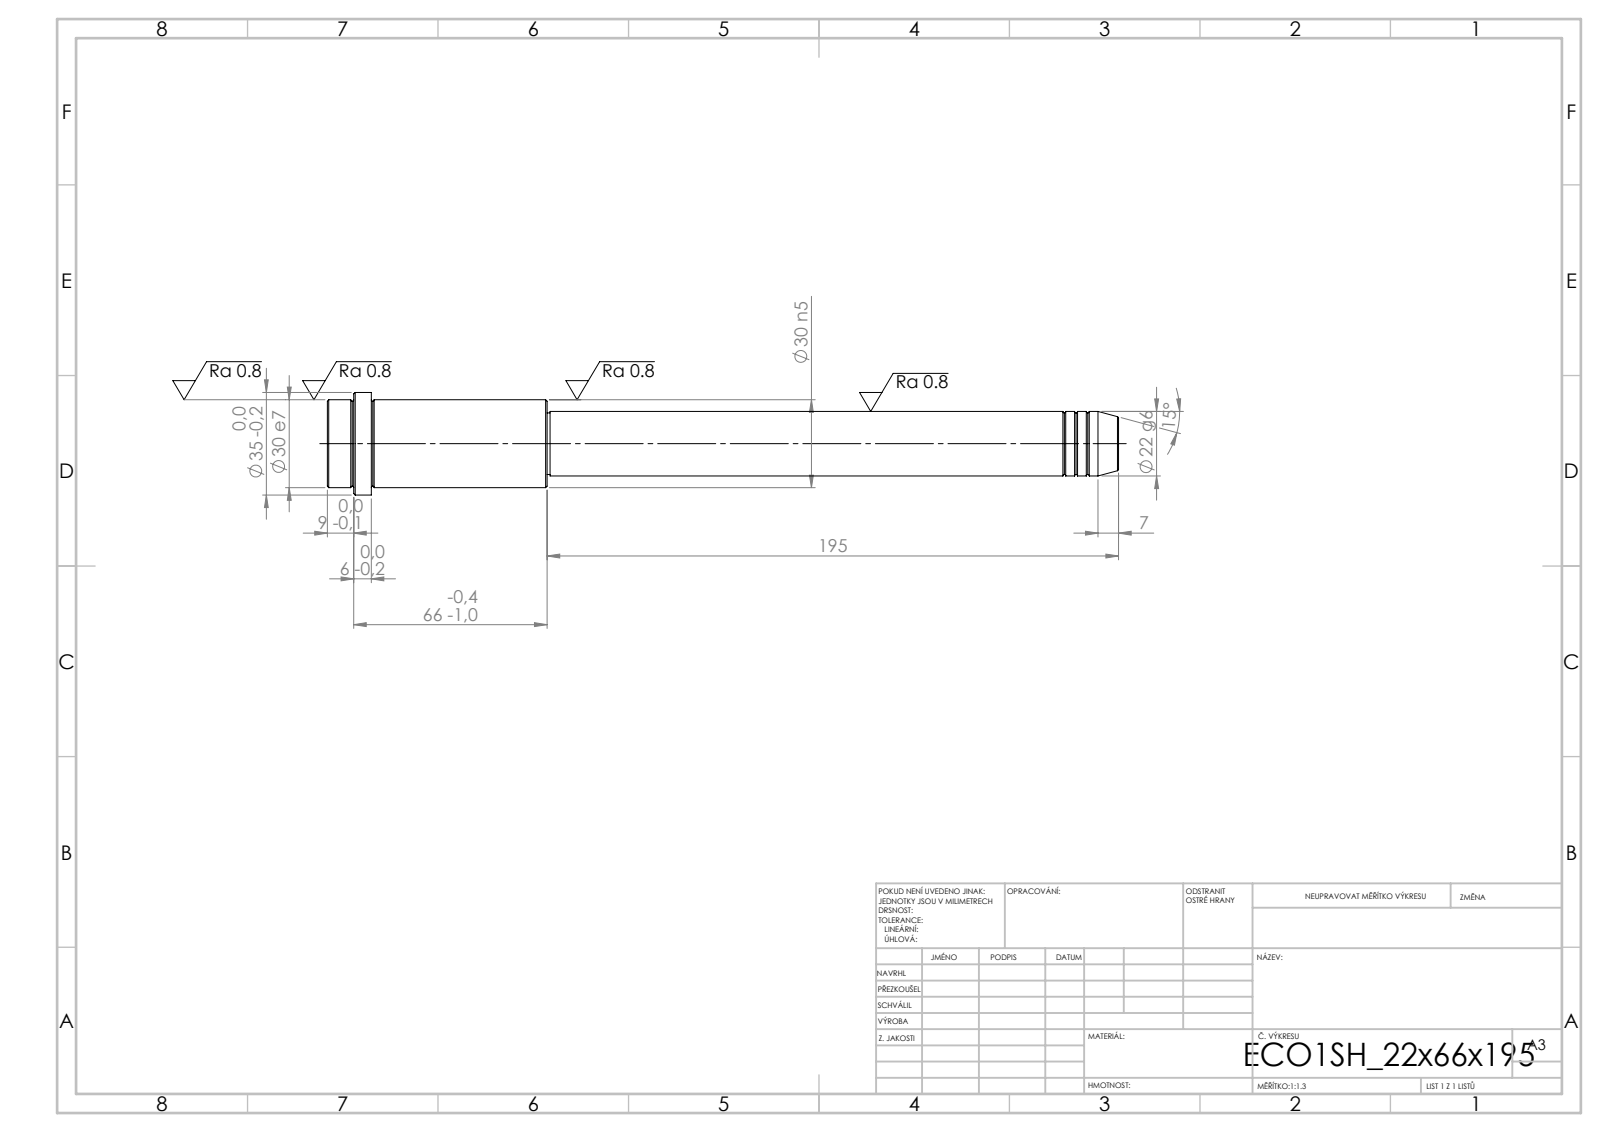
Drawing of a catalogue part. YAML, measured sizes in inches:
step_written_by: "SolidWorks 2019 (CONFIG_CONTROL_DESIGN)"
units: inches
bodies: {solids: 1, faces: 52, planar: 6, cylindrical: 16, other: 30}
overall_size: [10.63, 1.378, 1.378]
volume: 7.812
surface_area: 35.03
round_bosses_or_shafts:
  - {diameter: 1.378, count: 1}
  - {diameter: 1.181, count: 1}
  - {diameter: 0.866, count: 1}
  - {diameter: 0.827, count: 1}
face_to_face_distances: [2.953, 2.362, 0.591, 7.677, 10.039, 10.63, 10.276, 2.598, 0.236, 0.354]
